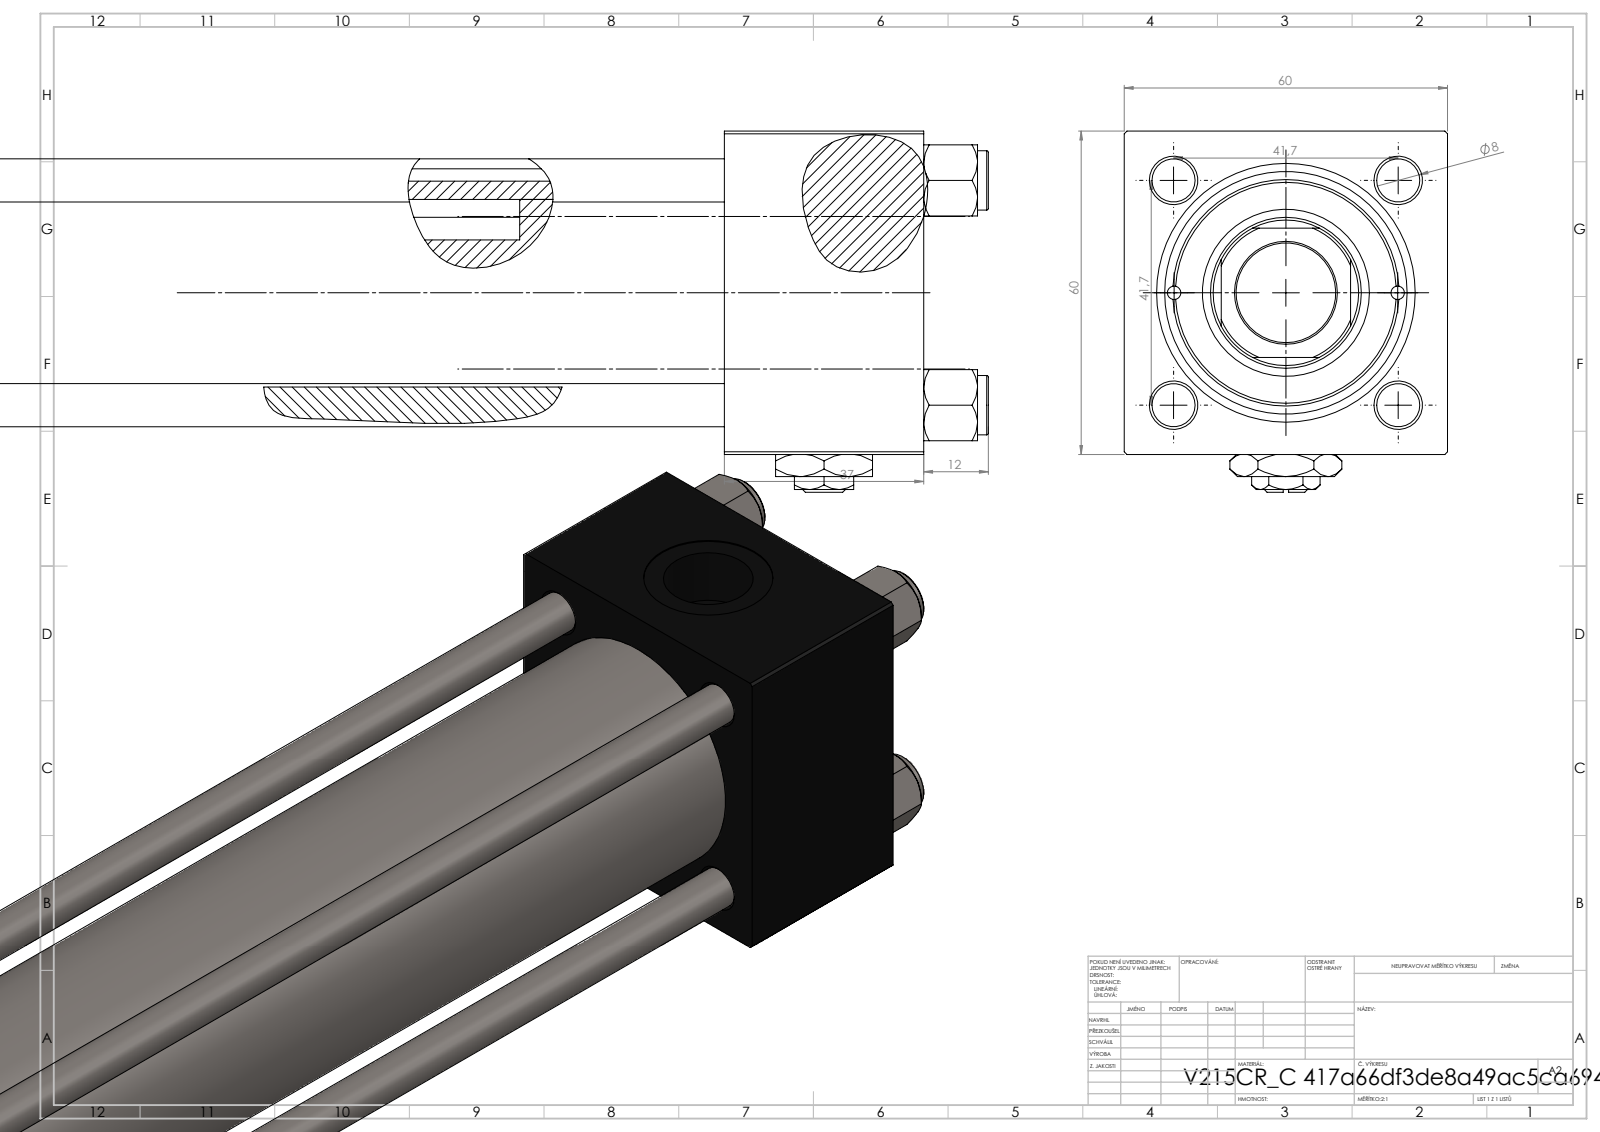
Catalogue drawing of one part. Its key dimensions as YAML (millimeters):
part_name: "V215CR_C_Body; V215CR_VCP_C; NUT_M5_C; V215_VC_A (+2 more)"
step_written_by: "SolidWorks 2019 (CONFIG_CONTROL_DESIGN)"
units: millimeters
bodies: {solids: 13, faces: 1256, planar: 576, cylindrical: 102, other: 578}
overall_size: [325, 67, 60]
volume: 591425
surface_area: 178777
round_holes:
  - {diameter: 8, count: 4}
  - {diameter: 2.5, count: 2}
  - {diameter: 7, count: 2}
  - {diameter: 16.66, count: 2}
  - {diameter: 24, count: 2}
  - {diameter: 18.5, count: 1}
  - {diameter: 28, count: 1}
  - {diameter: 31, count: 1}
  - {diameter: 40, count: 1}
  - {diameter: 45, count: 1}
round_bosses_or_shafts:
  - {diameter: 11, count: 4}
  - {diameter: 46, count: 1}
  - {diameter: 42, count: 1}
partial_cylinders:
  - {radius: 13.5, count: 1}
face_to_face_distances: [60, 37, 235, 198, 53, 259.3, 222.3, 24.3, 288, 251]
hole_center_spacings: [20.85, 29.49, 41.7, 46.53, 20.75, 58.97, 41.5, 232.5]
